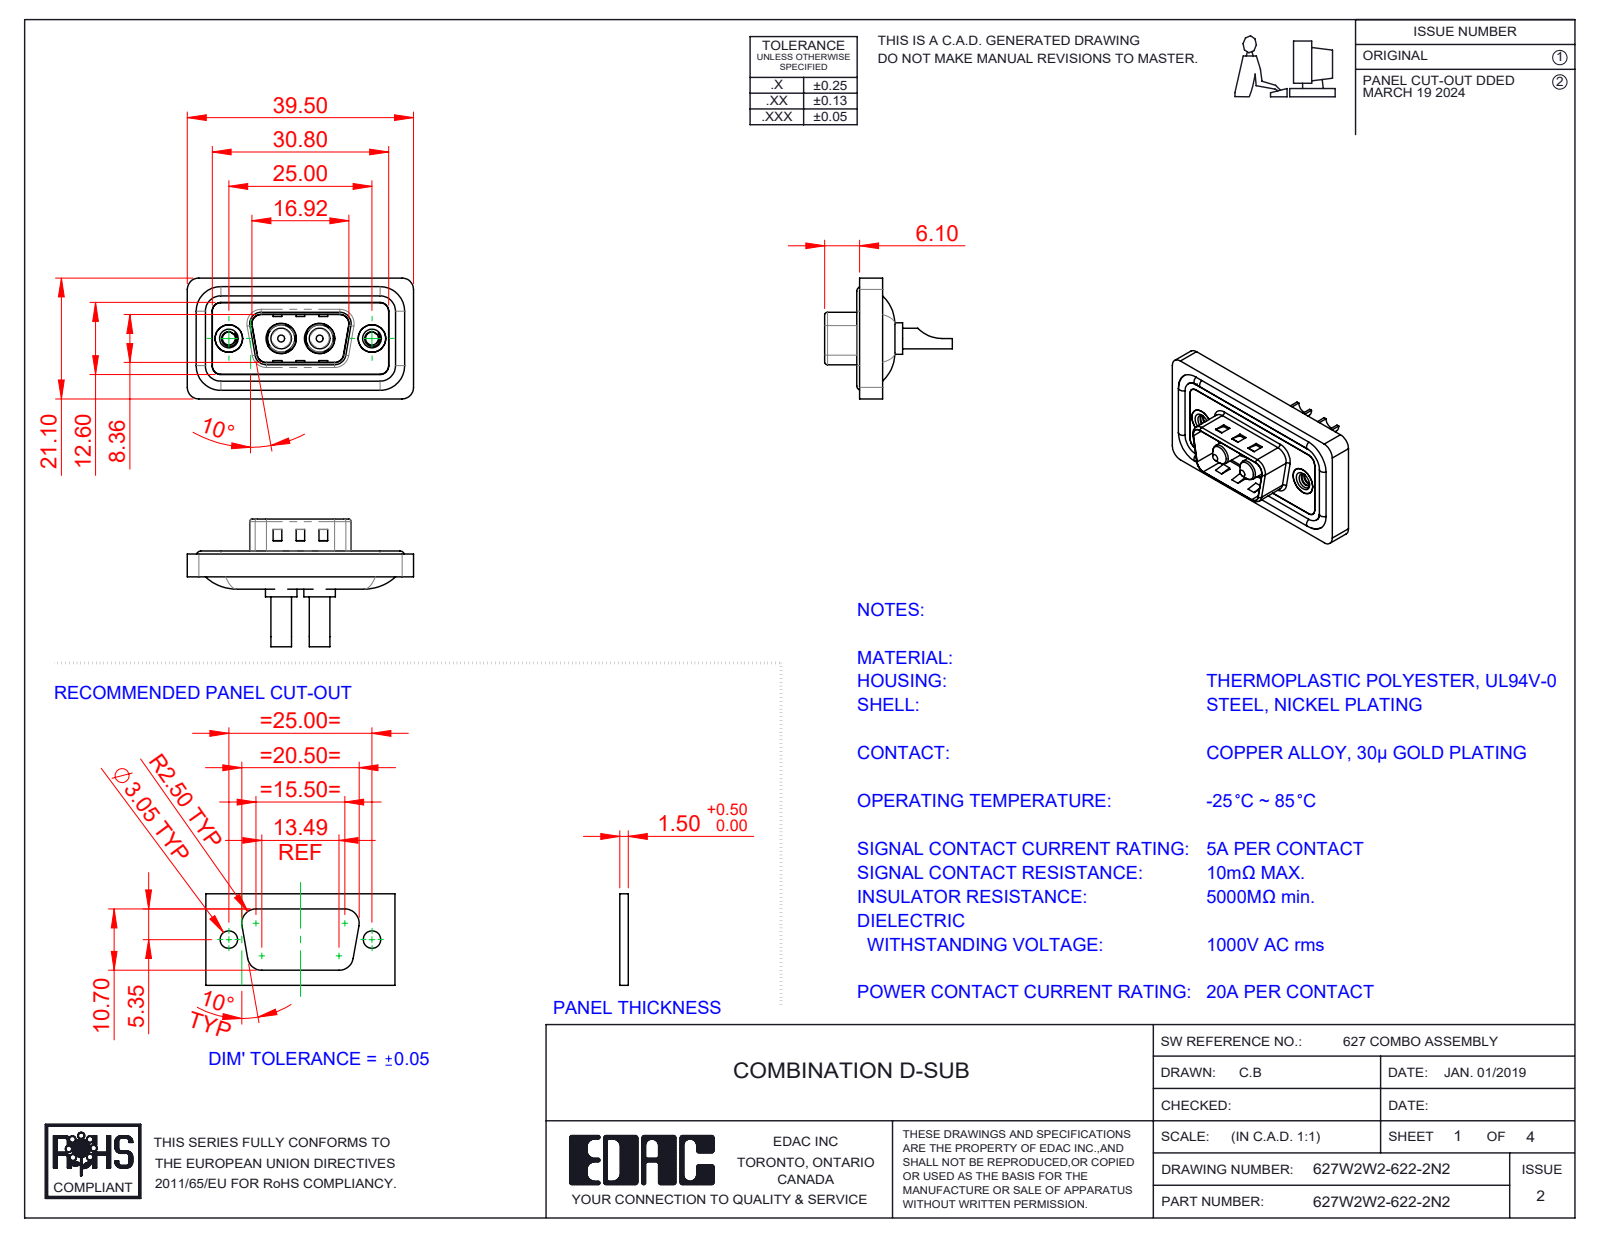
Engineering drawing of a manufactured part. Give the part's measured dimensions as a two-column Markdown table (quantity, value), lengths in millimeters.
| quantity | value |
| --- | --- |
| part name | 627Combo Shell Front_09 Contacts; 627Combo Waterproof Housing_09 Contacts; Power Pin_20A SC; 627Combo Threaded Rivet_2 (+3 more) |
| STEP written by | SolidWorks 2023 (CONFIG_CONTROL_DESIGN) |
| units | millimeters |
| bodies | 11 solids, 503 faces (171 planar, 224 cylindrical, 108 other) |
| overall size | 39.5 × 22.3 × 21.1 |
| volume | 4 486 mm³ |
| surface area | 7 149 mm² |
| round holes (diameter × count) | 2.26 × 2, 2.7 × 2, 4 × 2, 4.8 × 2, 4.85 × 2, 5 × 2, 5.3 × 2 |
| round bosses / shafts (diameter × count) | 1.6 × 4, 5.5 × 2, 5.2 × 2, 4.9 × 2, 4.75 × 2, 3.75 × 2, 3.6 × 2 |
| partial cylindrical surfaces (radius × count) | 1.5 × 22, 2 × 18, 0.5 × 8, 1.6 × 8, 0.25 × 4, 0.6 × 4, 0.65 × 4, 0.9 × 4 |
| main face-to-face distances | 0.4, 1.1, 2.9, 3.1, 0.5, 1.6, 1.5, 4, 2.5, 0.7 |
| hole center spacings | 9.14, 15.86, 6.72, 25 |
